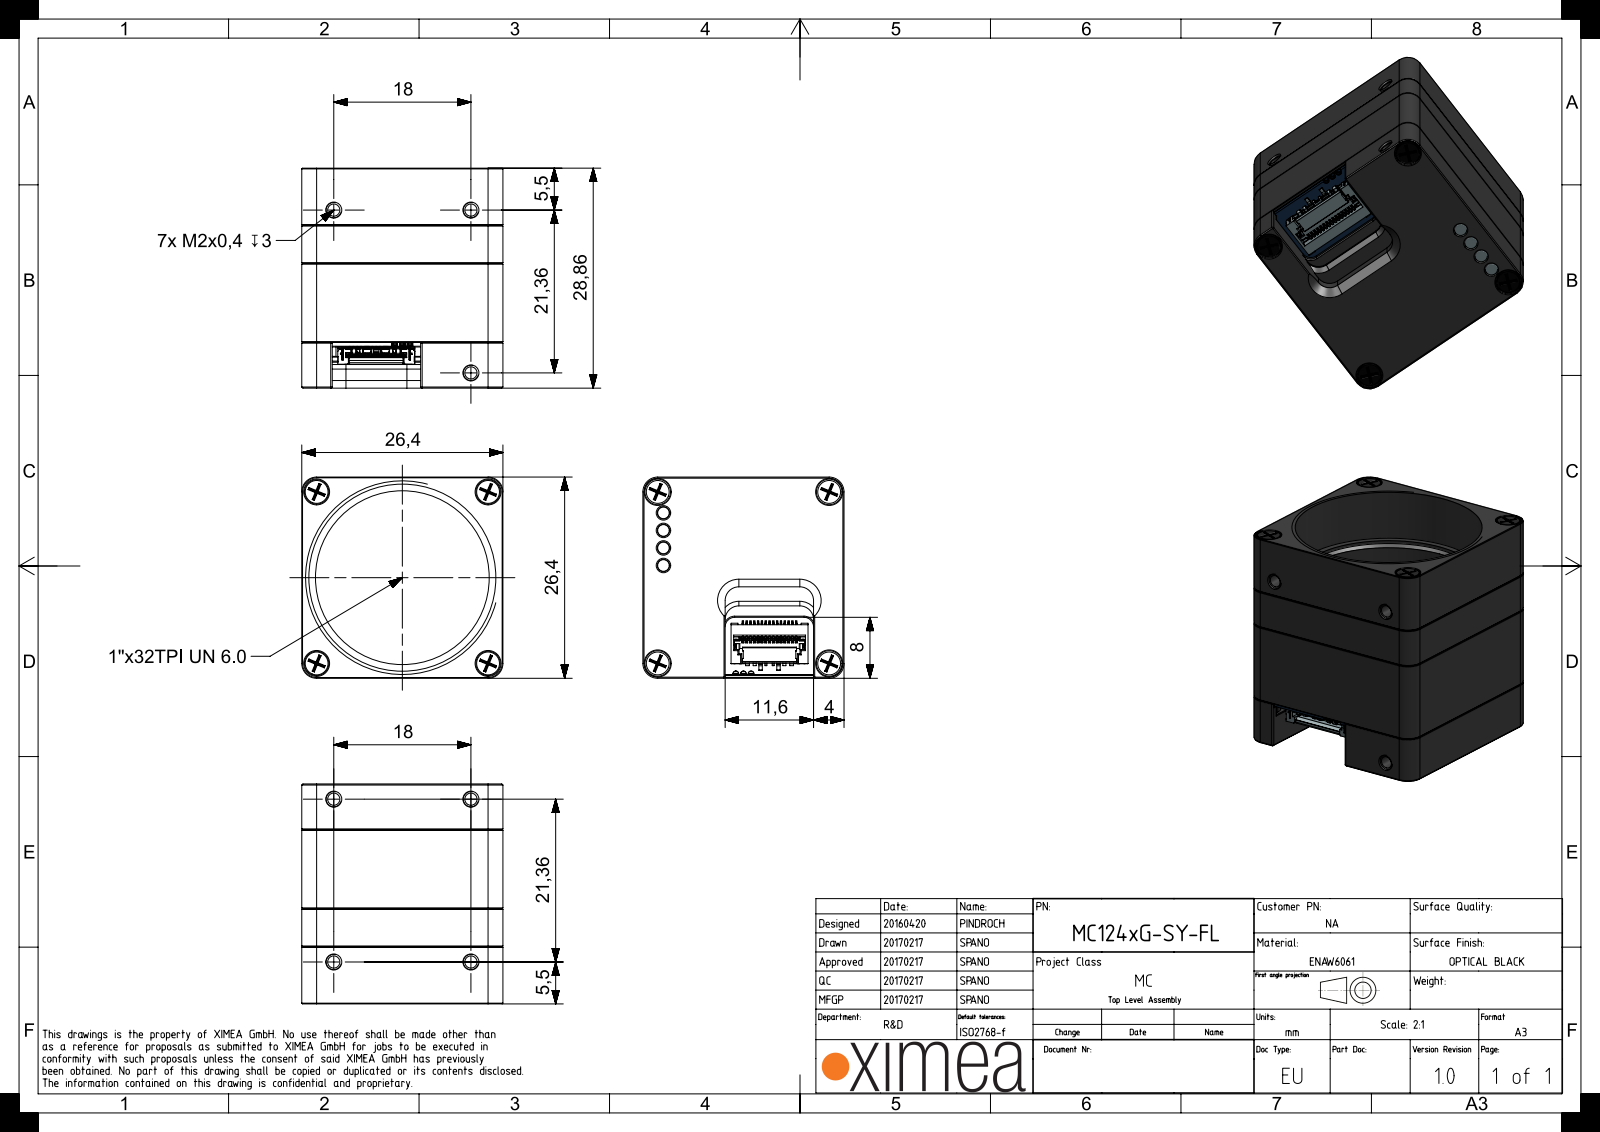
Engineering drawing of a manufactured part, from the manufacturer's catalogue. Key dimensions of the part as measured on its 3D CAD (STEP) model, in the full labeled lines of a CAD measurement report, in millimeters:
Part name (STEP PRODUCT): MT124xG-PR-SENSOR-PCA; MECH-O-RING-22X1-VI370; FLT-BK7-AR2X-D25; SROB-M1.6x3-SLOT-STNLS (+8 more)
STEP written by: SIEMENS PLM Software NX 1907 (AUTOMOTIVE_DESIGN)
Units: millimetres
Bodies: 31 solids, 7224 faces (4905 planar, 2024 cylindrical, 295 other)
Overall size (bounding box): 28.9 × 26.4 × 26.4
Volume: 9 780 mm³ · Surface area: 17 170 mm²
Round holes (diameter × count): ⌀1.6 ×12, ⌀1 ×4, ⌀2 ×4, ⌀2.1 ×4, ⌀3 ×4, ⌀3.2 ×4, ⌀3.4 ×4, ⌀1.3 ×2, ⌀1.7 ×2, ⌀4 ×1, ⌀21 ×1, ⌀22.8 ×1
Round bosses / shafts (diameter × count): ⌀1.9 ×4, ⌀1.6 ×4, ⌀0.8 ×4, ⌀3 ×2, ⌀1.6 ×2, ⌀25 ×1, ⌀21.6 ×1
Partial cylindrical surfaces — rounded edges, fillets, slot ends (radius × count): R1 ×26, R0.3 ×17, R0.1 ×14, R0.2 ×14, R0.2 ×12, R0.4 ×12, R0.3 ×8, R0.5 ×8
Main face-to-face distances: 1, 3.6, 26.4, 6.9, 2.5, 4.6, 11.5, 10.5, 10.4, 6.8
Hole centre spacings: 15.9, 22.5, 2.3, 3.8, 4.6, 13.5, 18, 18.7
